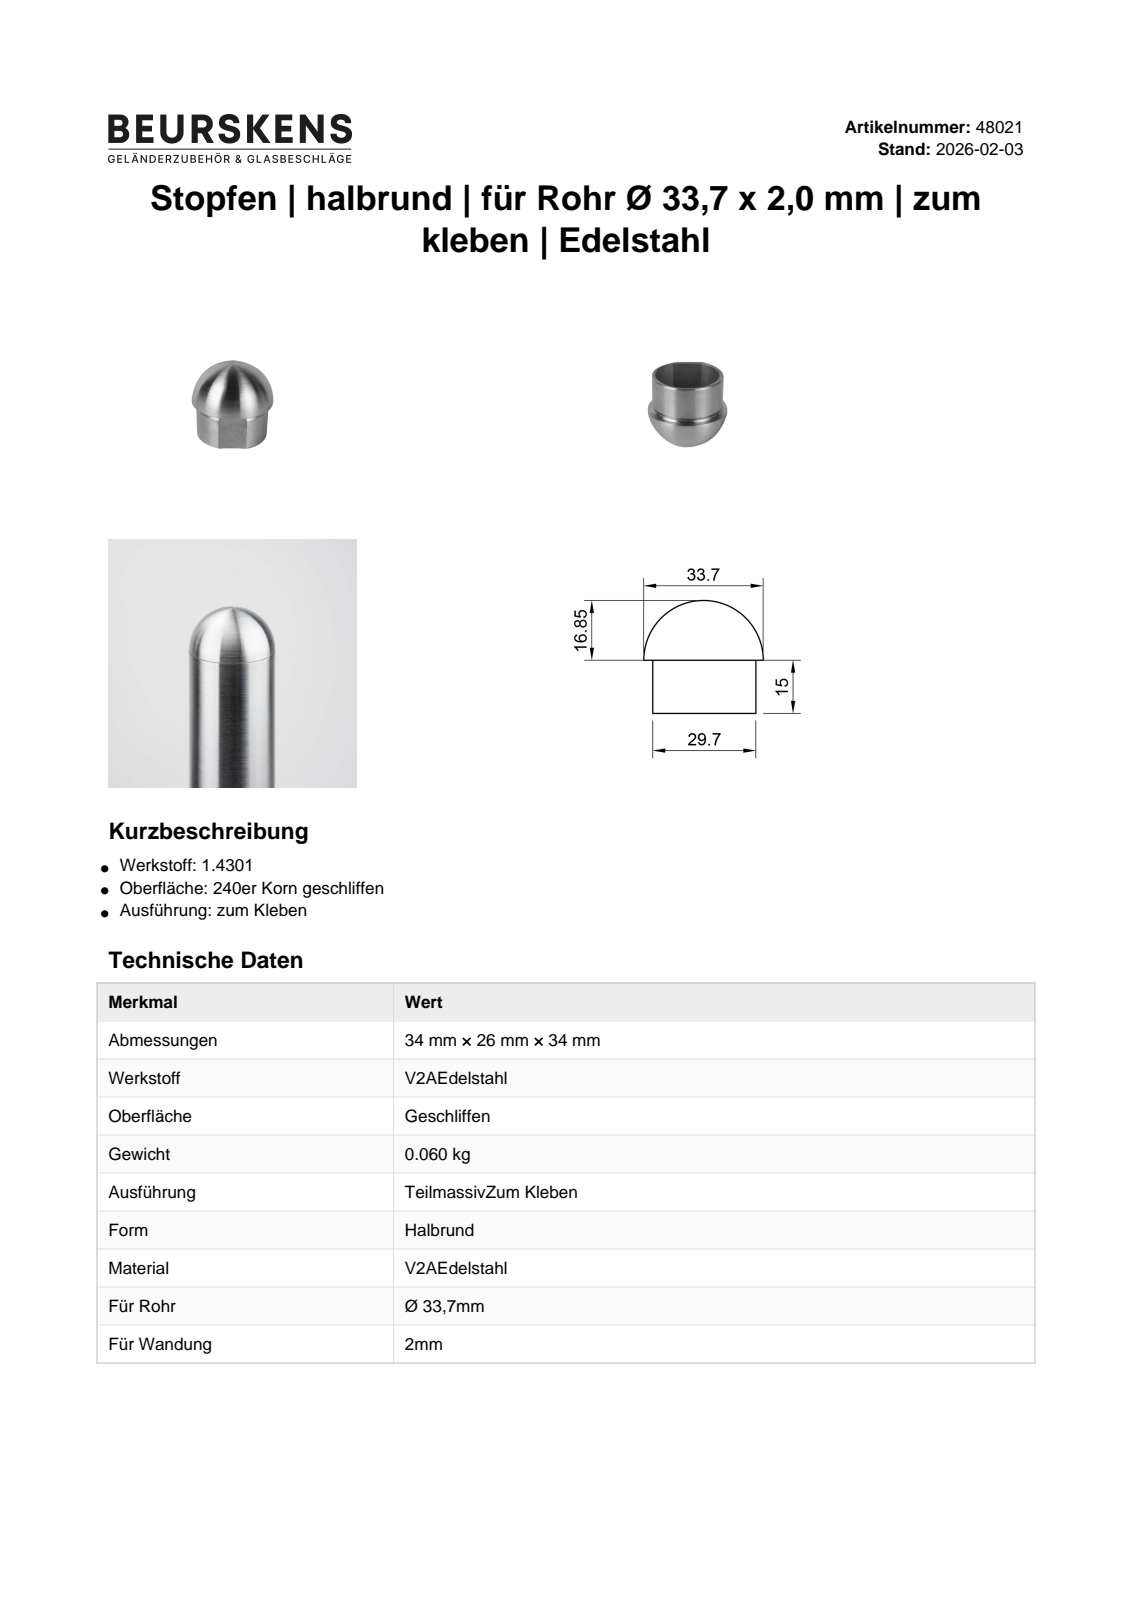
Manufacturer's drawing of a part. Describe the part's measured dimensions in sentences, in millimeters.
The part is named "48021". Its 3-D file was written by "Autodesk Inventor 2022 (AUTOMOTIVE_DESIGN)". It is 1 solid with 10 faces: 5 planar, 2 cylindrical and 3 other. Overall it measures 33.7 by 33.7 by 31.85 millimeters. Its volume is 4 687 cubic millimeters and its surface area 6 756 square millimeters. Round holes: 1 of diameter 25.6. Round bosses or shafts: 1 of diameter 29.6. The main face-to-face distances are 1, 15, 17, 2, 16.
